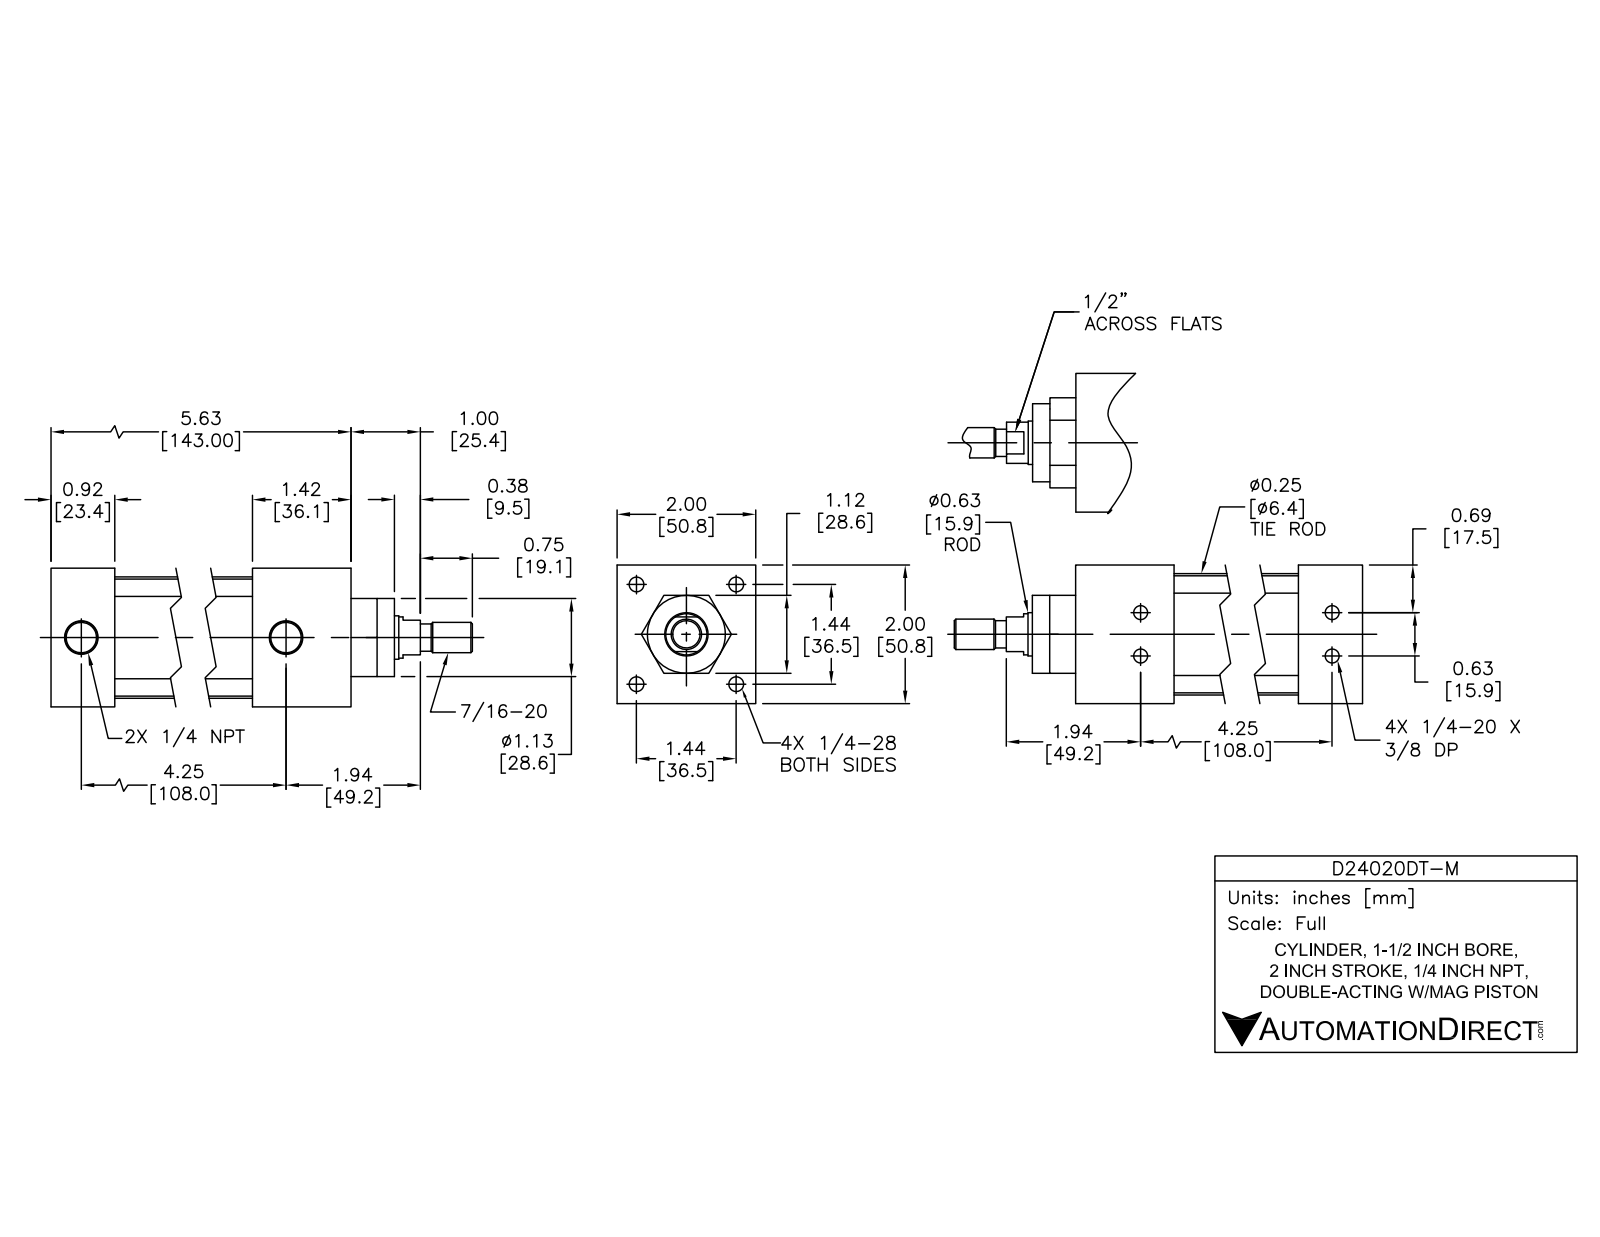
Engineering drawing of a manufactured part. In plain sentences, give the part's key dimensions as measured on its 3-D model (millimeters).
The part is named "D24020DT-M; D24020DT-M PISTON; D24020DT-M BODY". Its 3-D file was written by "SolidWorks 2015 (AUTOMOTIVE_DESIGN)". It is 12 solids with 303 faces: 99 planar, 114 cylindrical and 90 other. Overall it measures 187.2 by 50.8 by 50.8 millimeters. Its volume is 243 800 cubic millimeters and its surface area 79 350 square millimeters. Round holes: 4 of diameter 5, 4 of diameter 5.4, 4 of diameter 7.1, 4 of diameter 10.3, 2 of diameter 7.5, 2 of diameter 12.1, 1 of diameter 15.9, 1 of diameter 16, 1 of diameter 38.1. Round bosses or shafts: 4 of diameter 9.9, 4 of diameter 6.4, 4 of diameter 5.6, 1 of diameter 44.5, 1 of diameter 38, 1 of diameter 28.5, 1 of diameter 15.8, 1 of diameter 15. Partial cylindrical surfaces (rounded edges, fillets, slot ends): 4 of radius 5.1. The main face-to-face distances are 50.8, 142.8, 36.1, 106.7, 119.4, 83.3, 23.4, 28.5, 116.9, 80.8. The hole center spacings are 8, 25.8, 36.4, 15.9, 51.5, 107.9, 108.1, 108.1.
